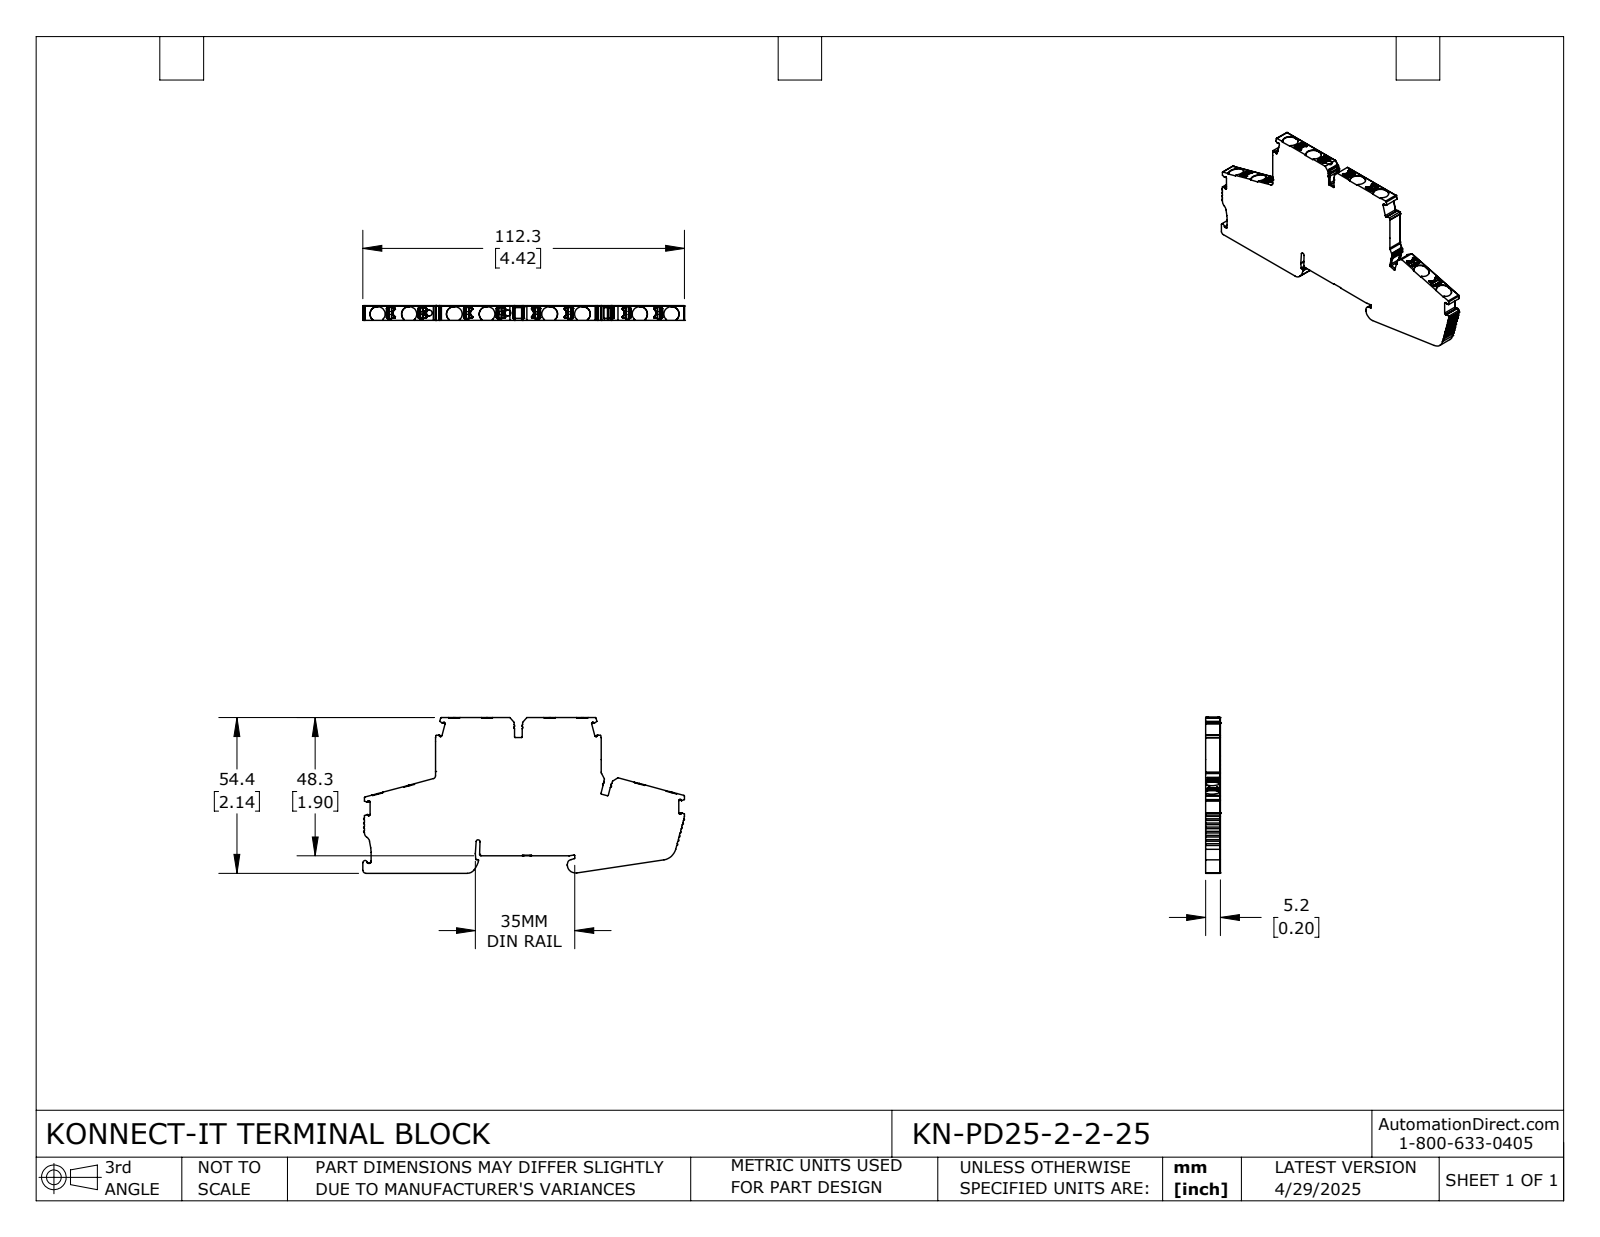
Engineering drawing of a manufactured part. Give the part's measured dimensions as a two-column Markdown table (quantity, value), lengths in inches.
| quantity | value |
| --- | --- |
| part name | KN-PD25-2-2-25 |
| STEP written by | SolidWorks 2024 (CONFIG_CONTROL_DESIGN) |
| units | inches |
| bodies | 1 solid, 1052 faces (494 planar, 422 cylindrical, 136 other) |
| overall size | 4.422 × 2.141 × 0.203 |
| volume | 1.357 in³ |
| surface area | 16.61 in² |
| round holes (diameter × count) | 0.083 × 2 |
| partial cylindrical surfaces (radius × count) | 0.008 × 98, 0.012 × 40, 0.004 × 37, 0.006 × 32, 0.02 × 17, 0.1 × 16, 0.016 × 10, 0.006 × 8 |
| main face-to-face distances | 0.203, 0.24, 2.141, 1.9, 1.893, 2.133, 2.279, 0.079, 0.197, 4.322 |
